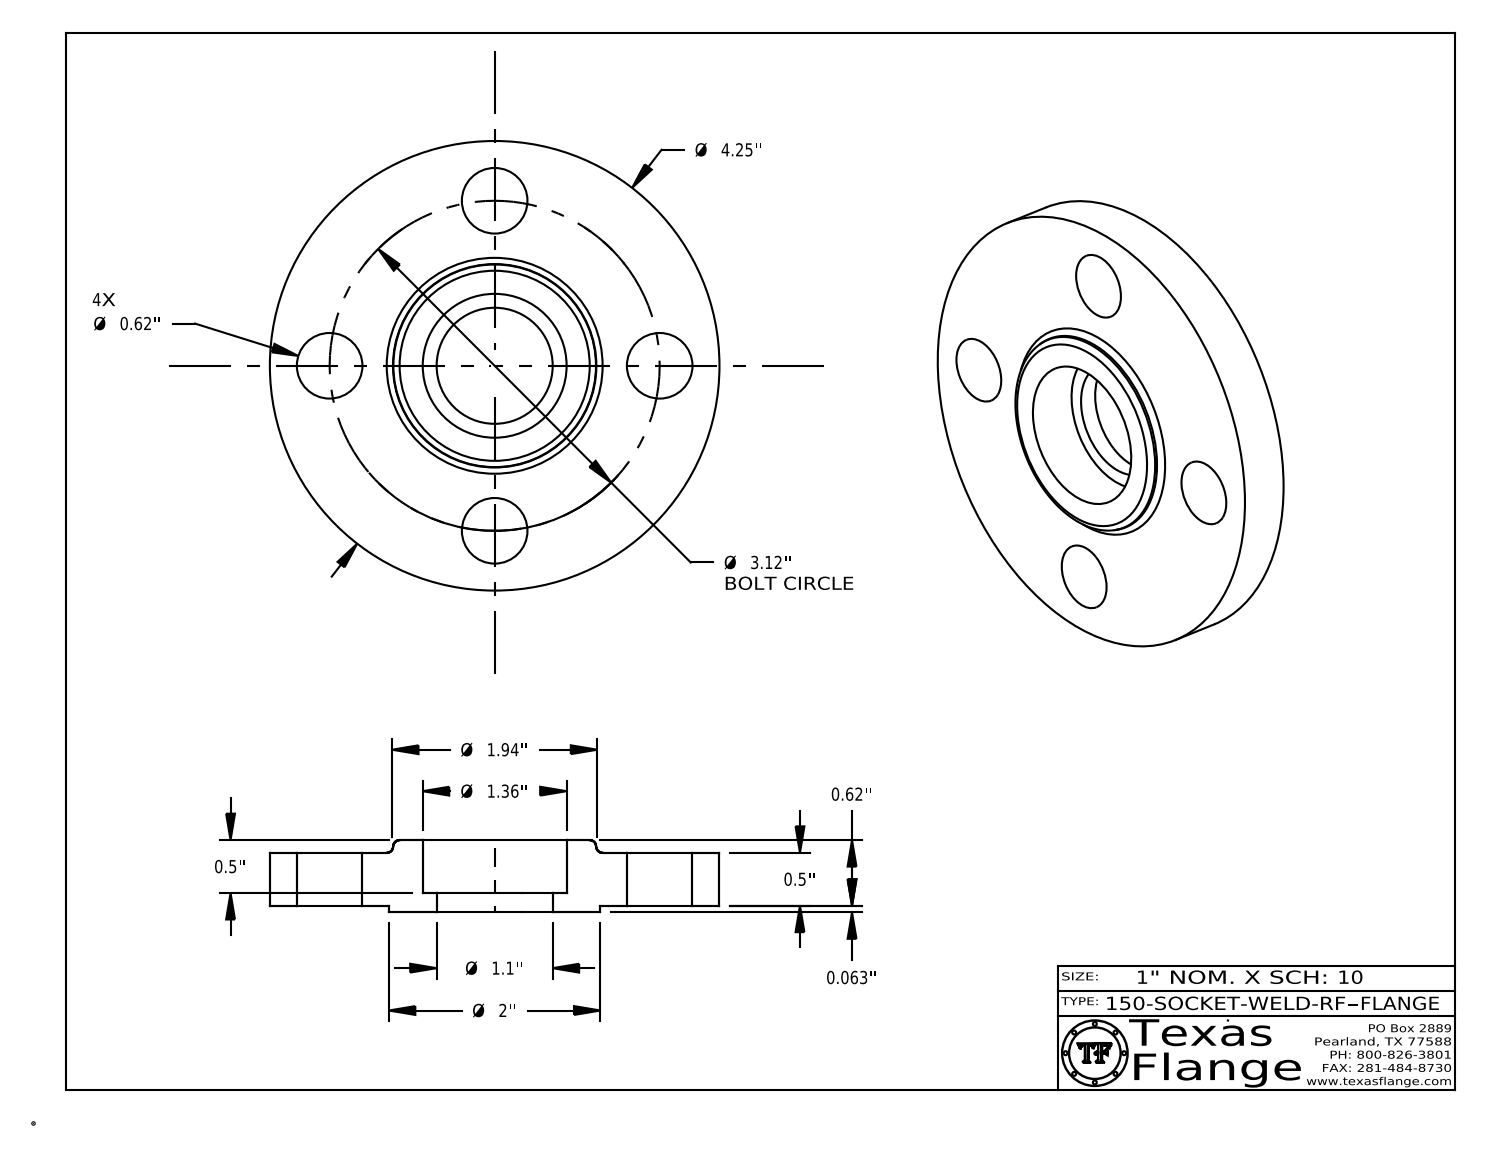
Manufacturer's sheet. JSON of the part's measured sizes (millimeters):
{"part_name": "150-SOCKET-WELD-RF", "step_written_by": "CATIA V5 STEP AP214 (AUTOMOTIVE_DESIGN)", "units": "millimeters", "bodies": {"solids": 1, "faces": 412, "planar": 370, "cylindrical": 36, "other": 6}, "overall_size": [108, 108, 17.3], "volume_mm3": 100500, "surface_area_mm2": 24700, "round_holes": [[15.7, 4], [12.6, 1], [27.9, 1], [34.5, 1]], "round_bosses_or_shafts": [[0.8, 8], [108, 1], [50.8, 1], [9.9, 1]], "face_to_face_distances": [12.7, 1.6, 14.3, 3, 17.3, 15.7, 4.6, 9.7, 13.9, 12.3], "hole_center_spacings": [39.6, 56, 30.3, 73.2, 79.2, 39.6]}
